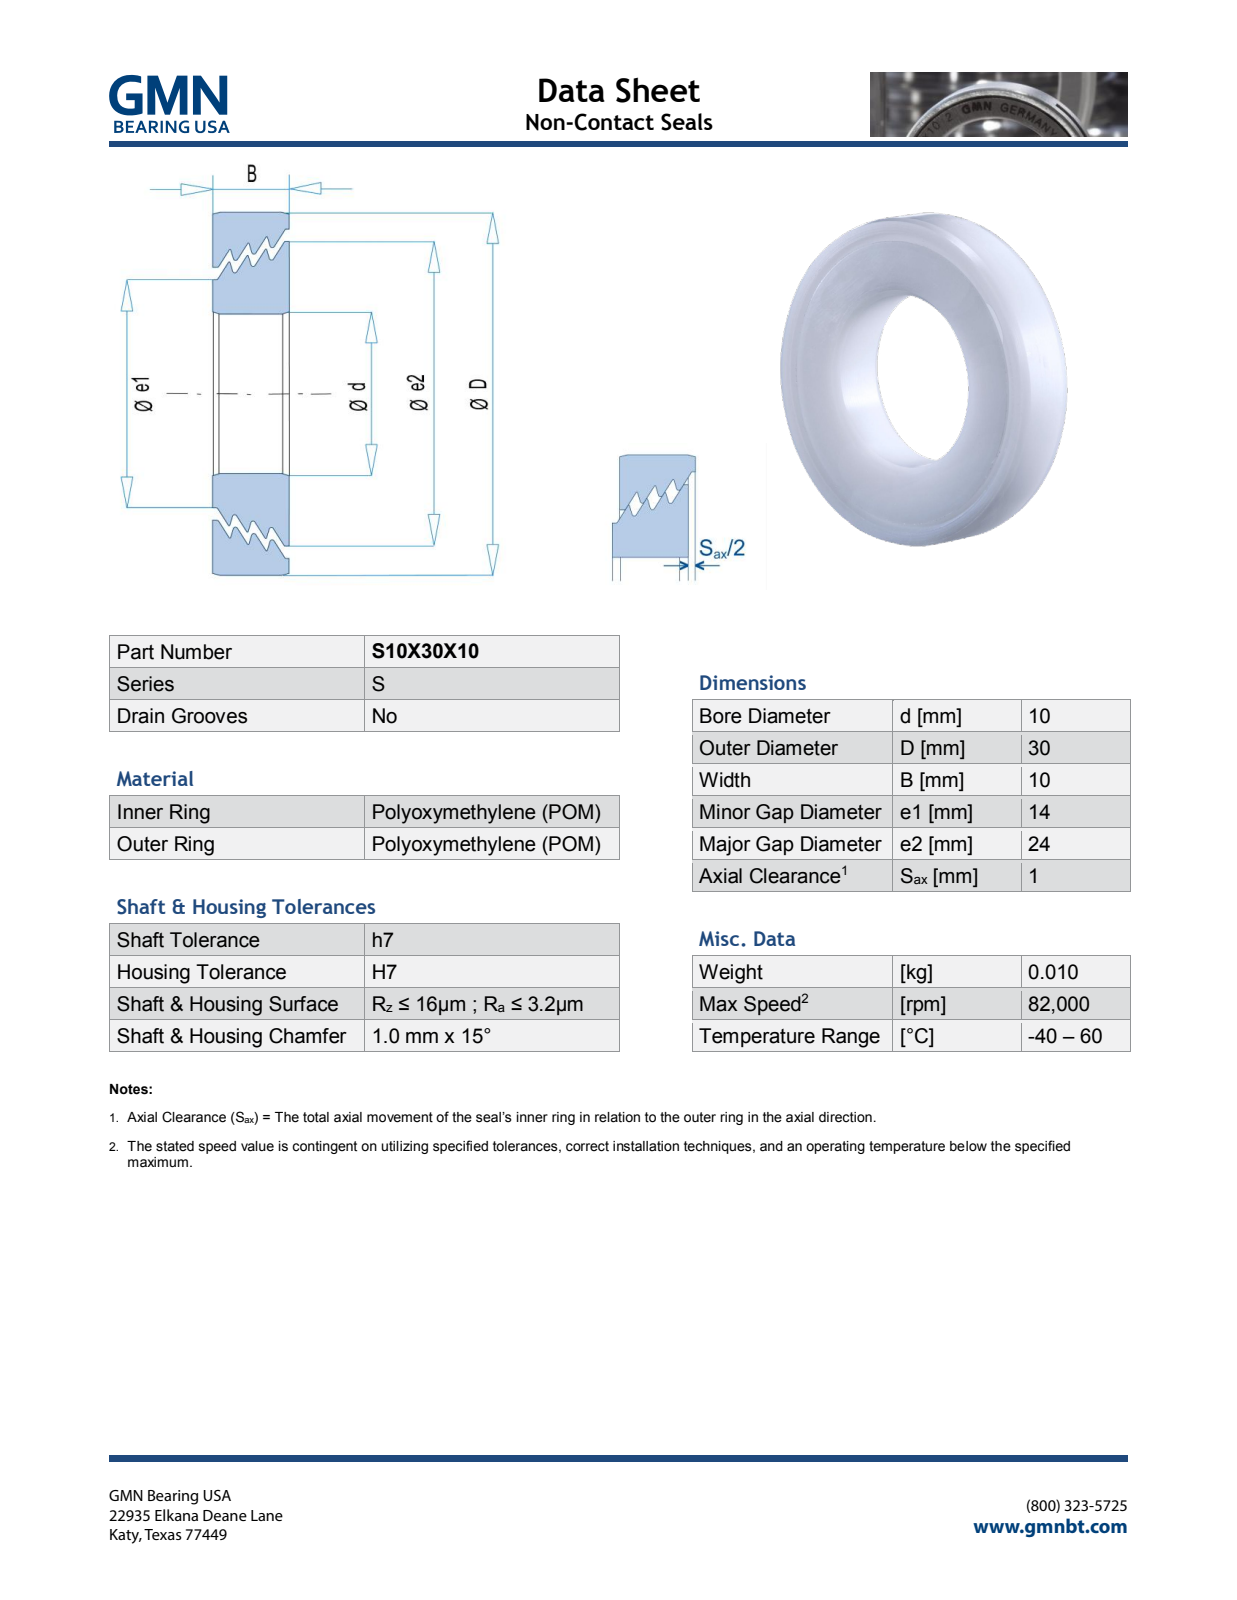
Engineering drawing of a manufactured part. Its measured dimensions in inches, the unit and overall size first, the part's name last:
Units: inches
Overall size (bounding box): 1.181 × 1.181 × 0.396
Round holes (diameter × count): ⌀0.394 ×1, ⌀0.615 ×1, ⌀1.009 ×1
Round bosses / shafts (diameter × count): ⌀1.181 ×1, ⌀0.945 ×1, ⌀0.551 ×1
Main face-to-face distances: 0.394, 0.396, 0.072, 0.063, 0.051, 0.063, 0.072, 0.054, 0.06, 0.031
Volume: 0.35 in³ · Surface area: 7.648 in²
Bodies: 2 solids, 651 faces (571 planar, 12 cylindrical, 68 other)
Part name (STEP PRODUCT): S10X30X10_PRT
STEP written by: PRO/ENGINEER BY PARAMETRIC TECHNOLOGY CORPORATION, 2013150 (AUTOMOTIVE_DESIGN)
